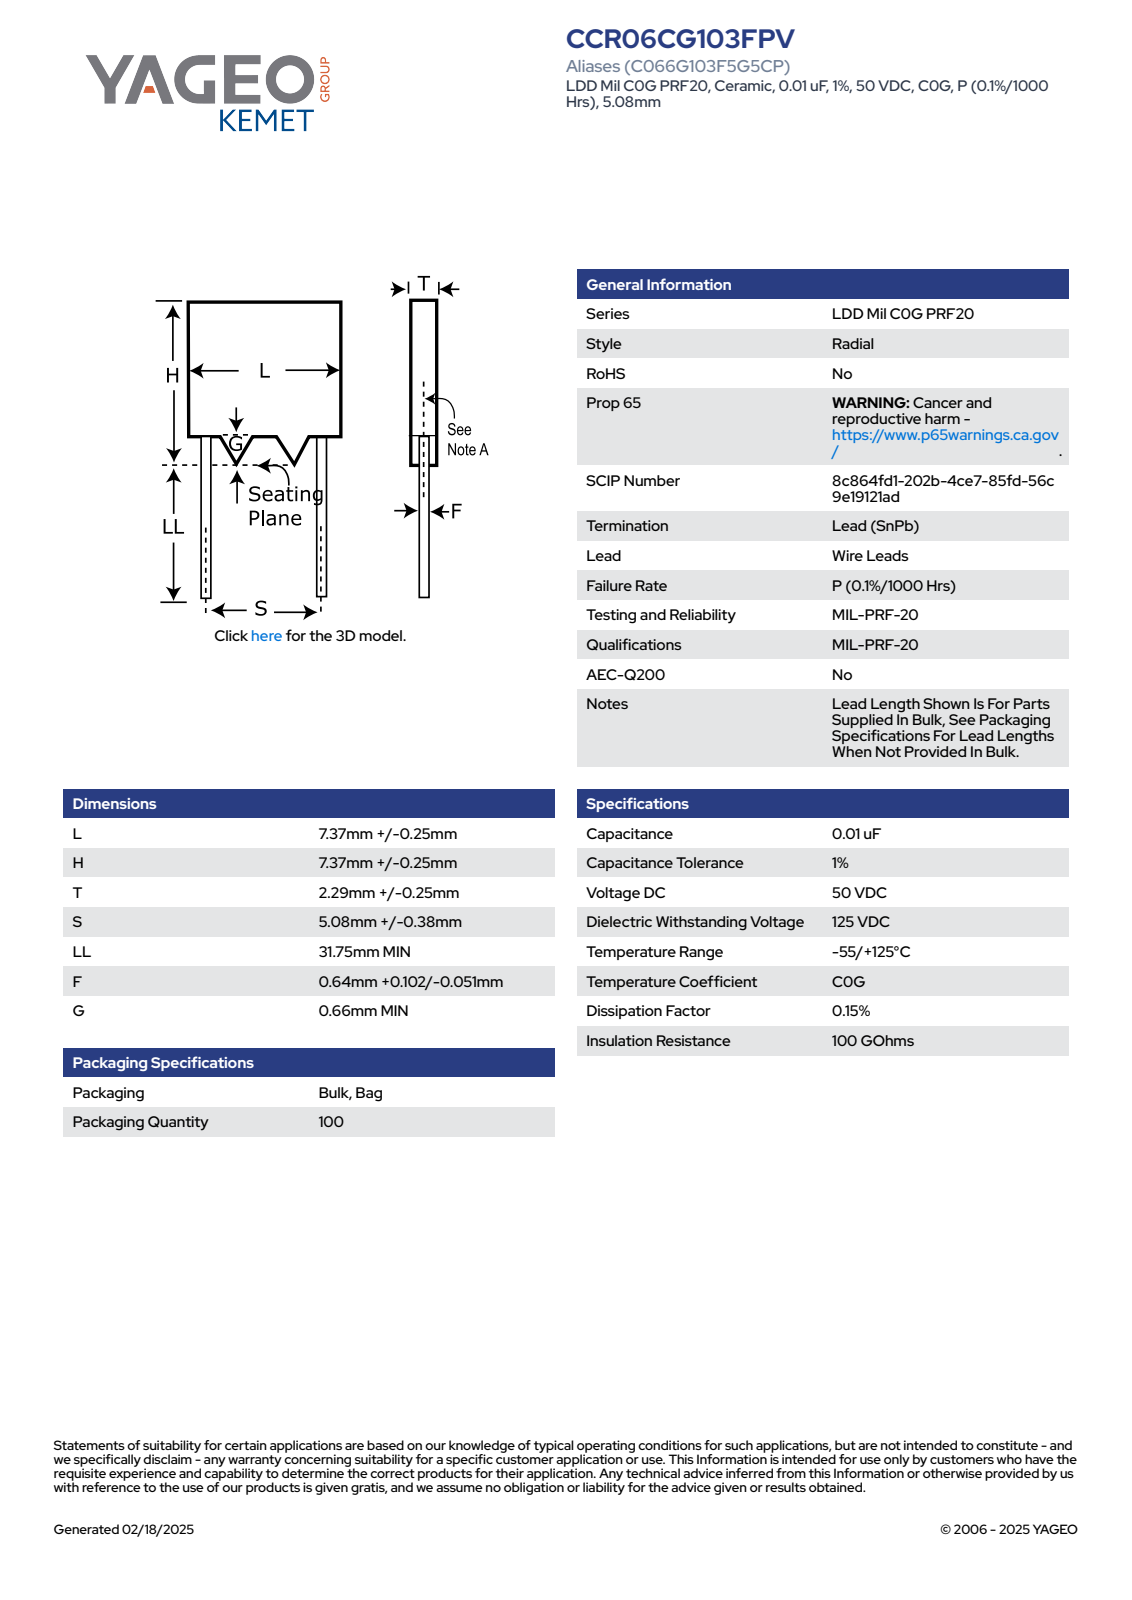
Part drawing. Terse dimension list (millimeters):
name: CCRM_V_C066_L7.62H7.62T2.54S5.08LL31.75F0.742G0.66
written by: SolidWorks 2014 (AUTOMOTIVE_DESIGN)
unit: mm
bodies: 4 solids, 75 faces (71 planar, 4 cylindrical, 0 other)
size: 38.46 × 7.62 × 2.54
volume: 161 mm³; area: 339 mm²
bosses: 2× ⌀0.74
face distances: 2.54, 7.62, 6.71, 2.01, 31.75, 38.46, 1.21, 35.7, 3.95, 2.76
